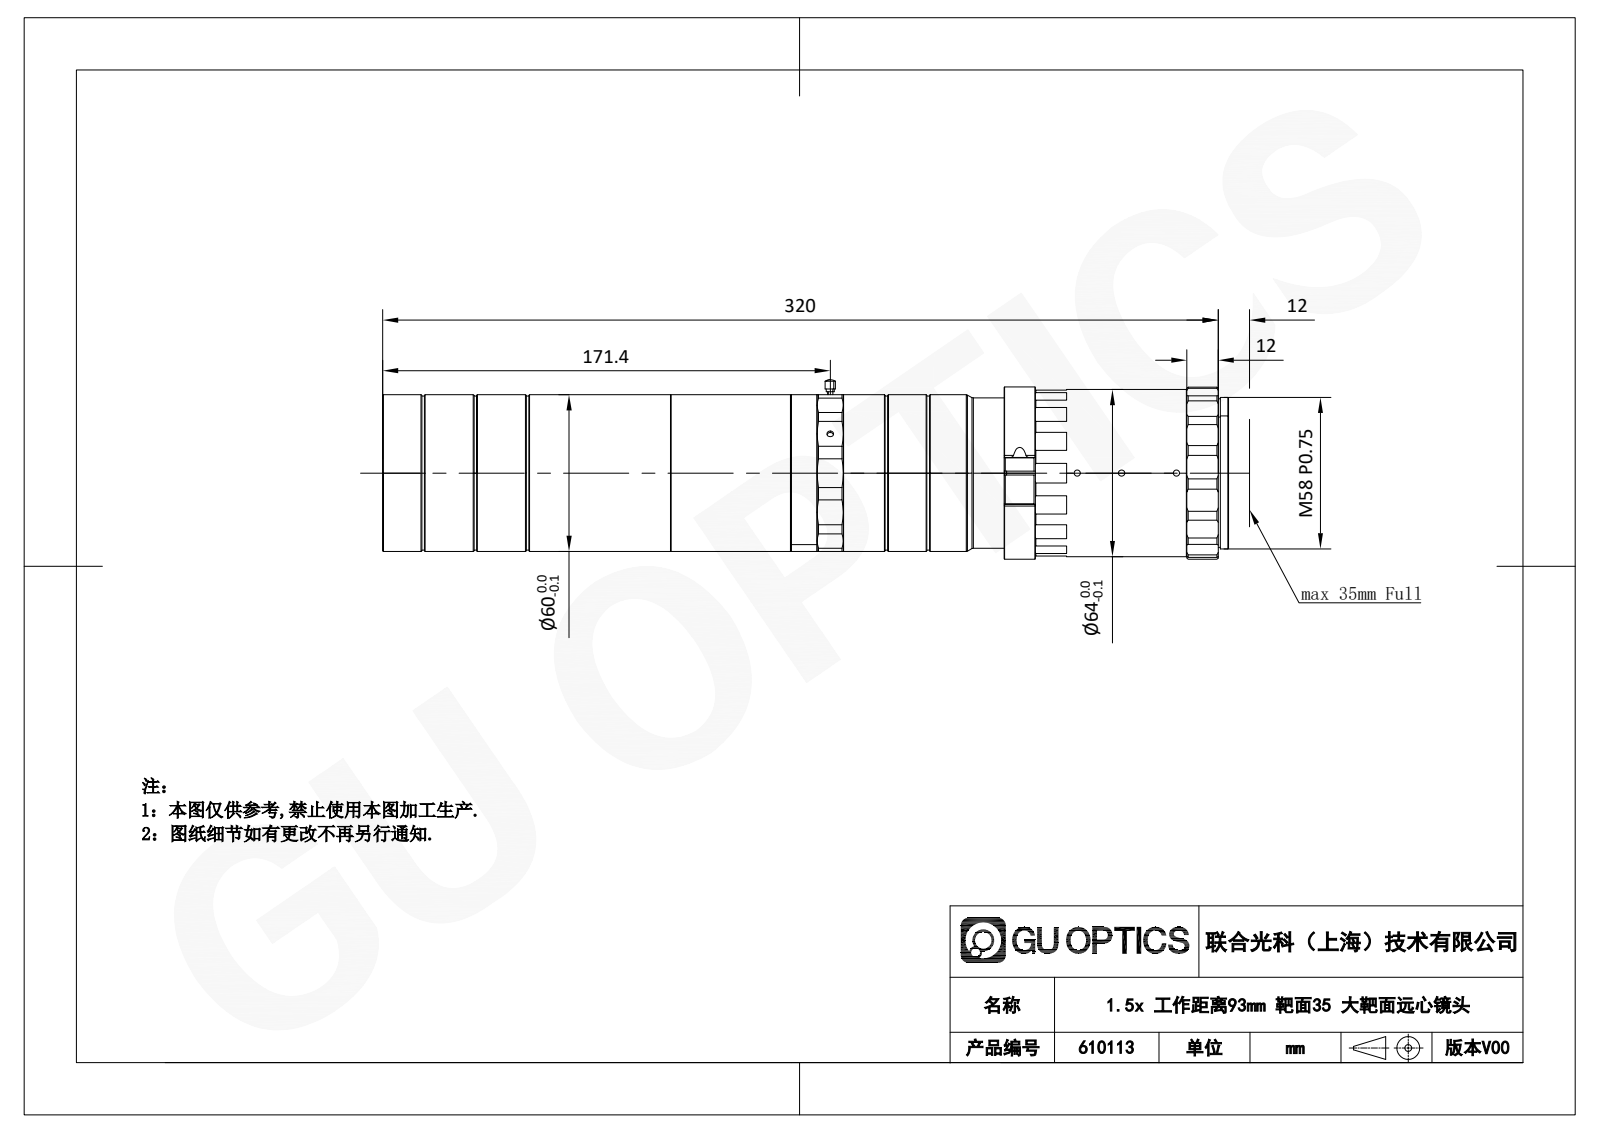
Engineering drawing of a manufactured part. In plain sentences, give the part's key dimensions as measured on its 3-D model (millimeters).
The part is named "DTCA35F-29.3-G-M58-AL". Its 3-D file was written by "SolidWorks 2017 (CONFIG_CONTROL_DESIGN)". It is 1 solid with 510 faces: 100 planar, 207 cylindrical and 203 other. Overall it measures 323.95 by 72.49 by 68.77 millimeters. Its volume is 879 289 cubic millimeters and its surface area 87 880 square millimeters. Round holes: 9 of diameter 2.4, 3 of diameter 2.5, 1 of diameter 2.2, 1 of diameter 3.4, 1 of diameter 4.5, 1 of diameter 52.5, 1 of diameter 54.5, 1 of diameter 55.5, 1 of diameter 56.5, 1 of diameter 57.5, 1 of diameter 57.9, 1 of diameter 58. Round bosses or shafts: 1 of diameter 66, 1 of diameter 64, 1 of diameter 62, 1 of diameter 61, 1 of diameter 60, 1 of diameter 59, 1 of diameter 57.82, 1 of diameter 56.8. Partial cylindrical surfaces (rounded edges, fillets, slot ends): 32 of radius 15, 2 of radius 1, 1 of radius 1.55, 1 of radius 4, 1 of radius 39.5. The main face-to-face distances are 82, 12, 60, 50, 20, 24, 62, 70, 237.95, 319.95. The hole center spacings are 17, 21, 38, 80.77.
